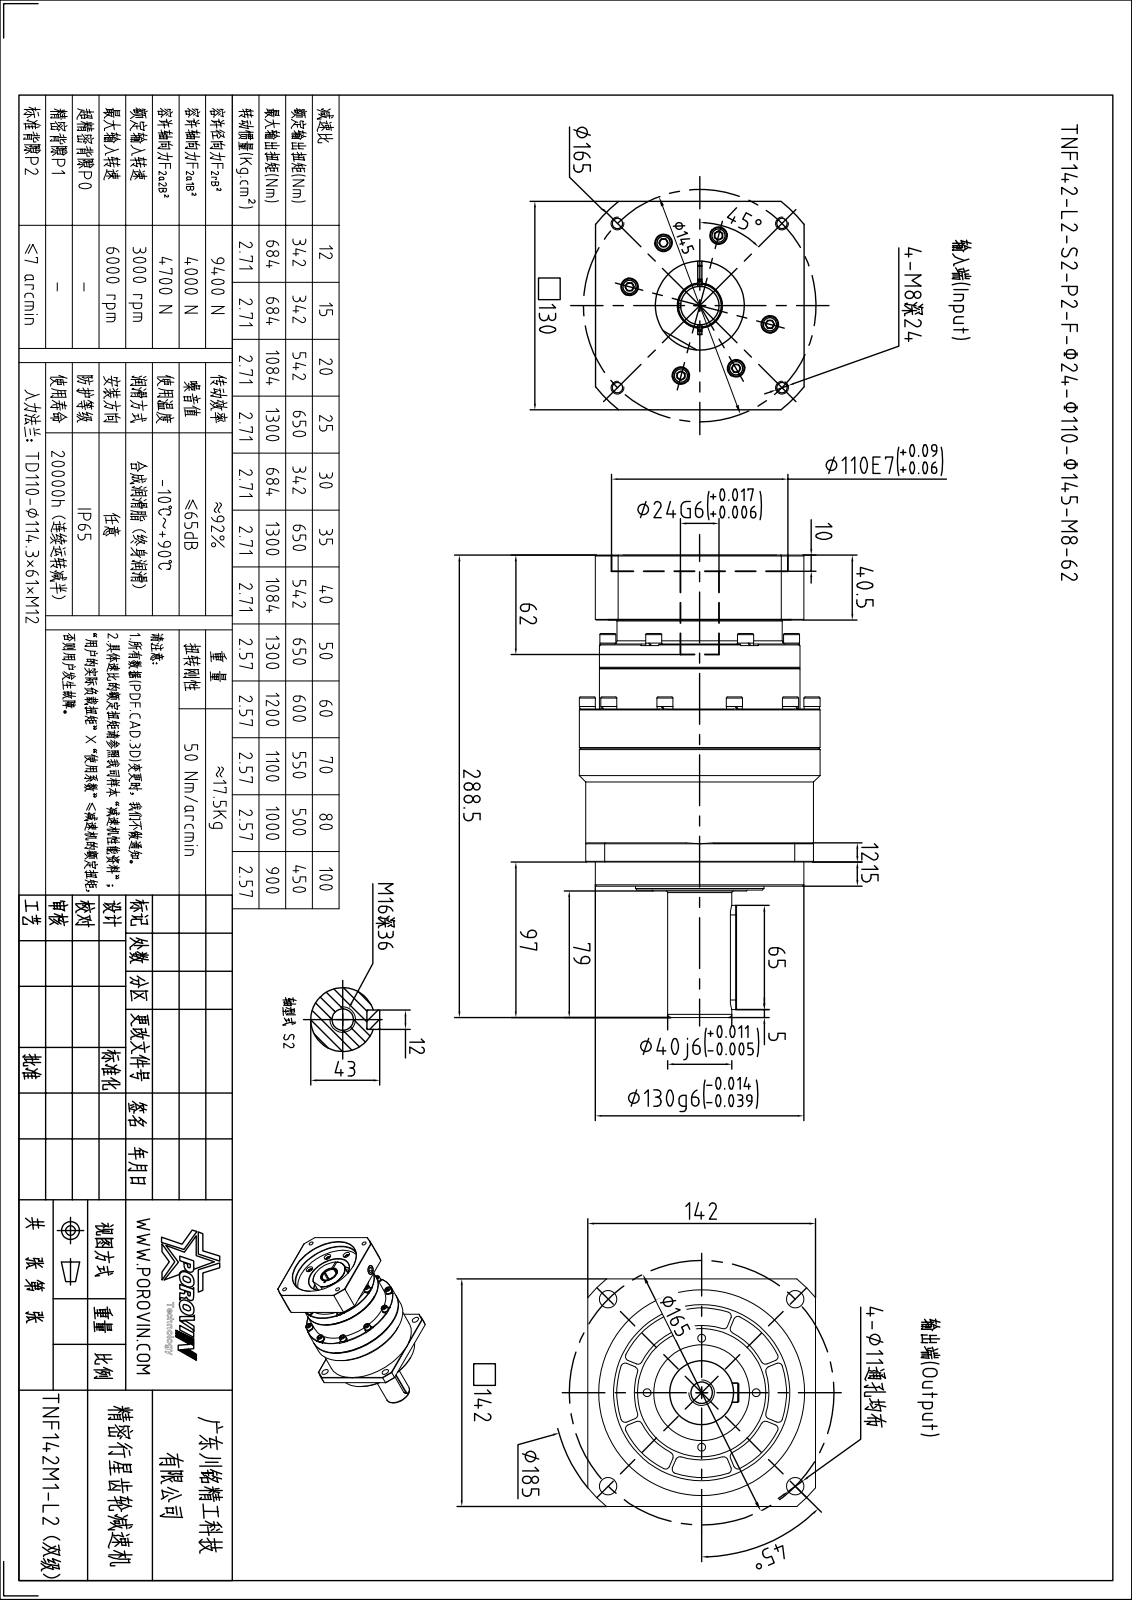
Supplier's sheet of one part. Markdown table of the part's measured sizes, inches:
| quantity | value |
| --- | --- |
| part name | hex socket set screws with flat point gb_GB_FASTENER_SCREWS_HSFP M16X16-N; hexagon socket head cap screws gb_GB_FASTENER_SCREWS_HSHCS M6X20-N; hexagon socket head cap screws gb_GB_FASTENER_SCREWS_HSHCS M6X25-N; hexagon socket head cap screws gb_GB_FASTENER_SCREWS_HSHCS M6X35-N (+3 more) |
| STEP written by | SolidWorks 2016 (CONFIG_CONTROL_DESIGN) |
| units | inches |
| bodies | 51 solids, 1327 faces (582 planar, 468 cylindrical, 277 other) |
| overall size | 11.358 × 5.906 × 5.906 |
| volume | 177.4 in³ |
| surface area | 470.8 in² |
| round holes (diameter × count) | 0.26 × 22, 0.263 × 22, 0.197 × 16, 0.433 × 10, 0.268 × 5, 0.354 × 1, 0.535 × 1, 0.551 × 1, 0.669 × 1, 0.945 × 1, 0.953 × 1, 2.756 × 1 |
| round bosses / shafts (diameter × count) | 0.394 × 22, 0.389 × 22, 0.236 × 22, 5.906 × 1, 5.591 × 1, 5.118 × 1, 4.921 × 1, 4.055 × 1 |
| partial cylindrical surfaces (radius × count) | 0.079 × 32, 0.217 × 6, 0.236 × 2, 0.276 × 1, 1.673 × 1, 2.008 × 1, 3.248 × 1, 3.642 × 1 |
| main face-to-face distances | 1.969, 1.181, 3.15, 5.354, 0.591, 1.594, 5.945, 5.118, 2.185, 7.539 |
| hole center spacings | 2.254, 2.756, 1.703, 2.474, 3.24, 4.333, 1.378, 3.441 |
